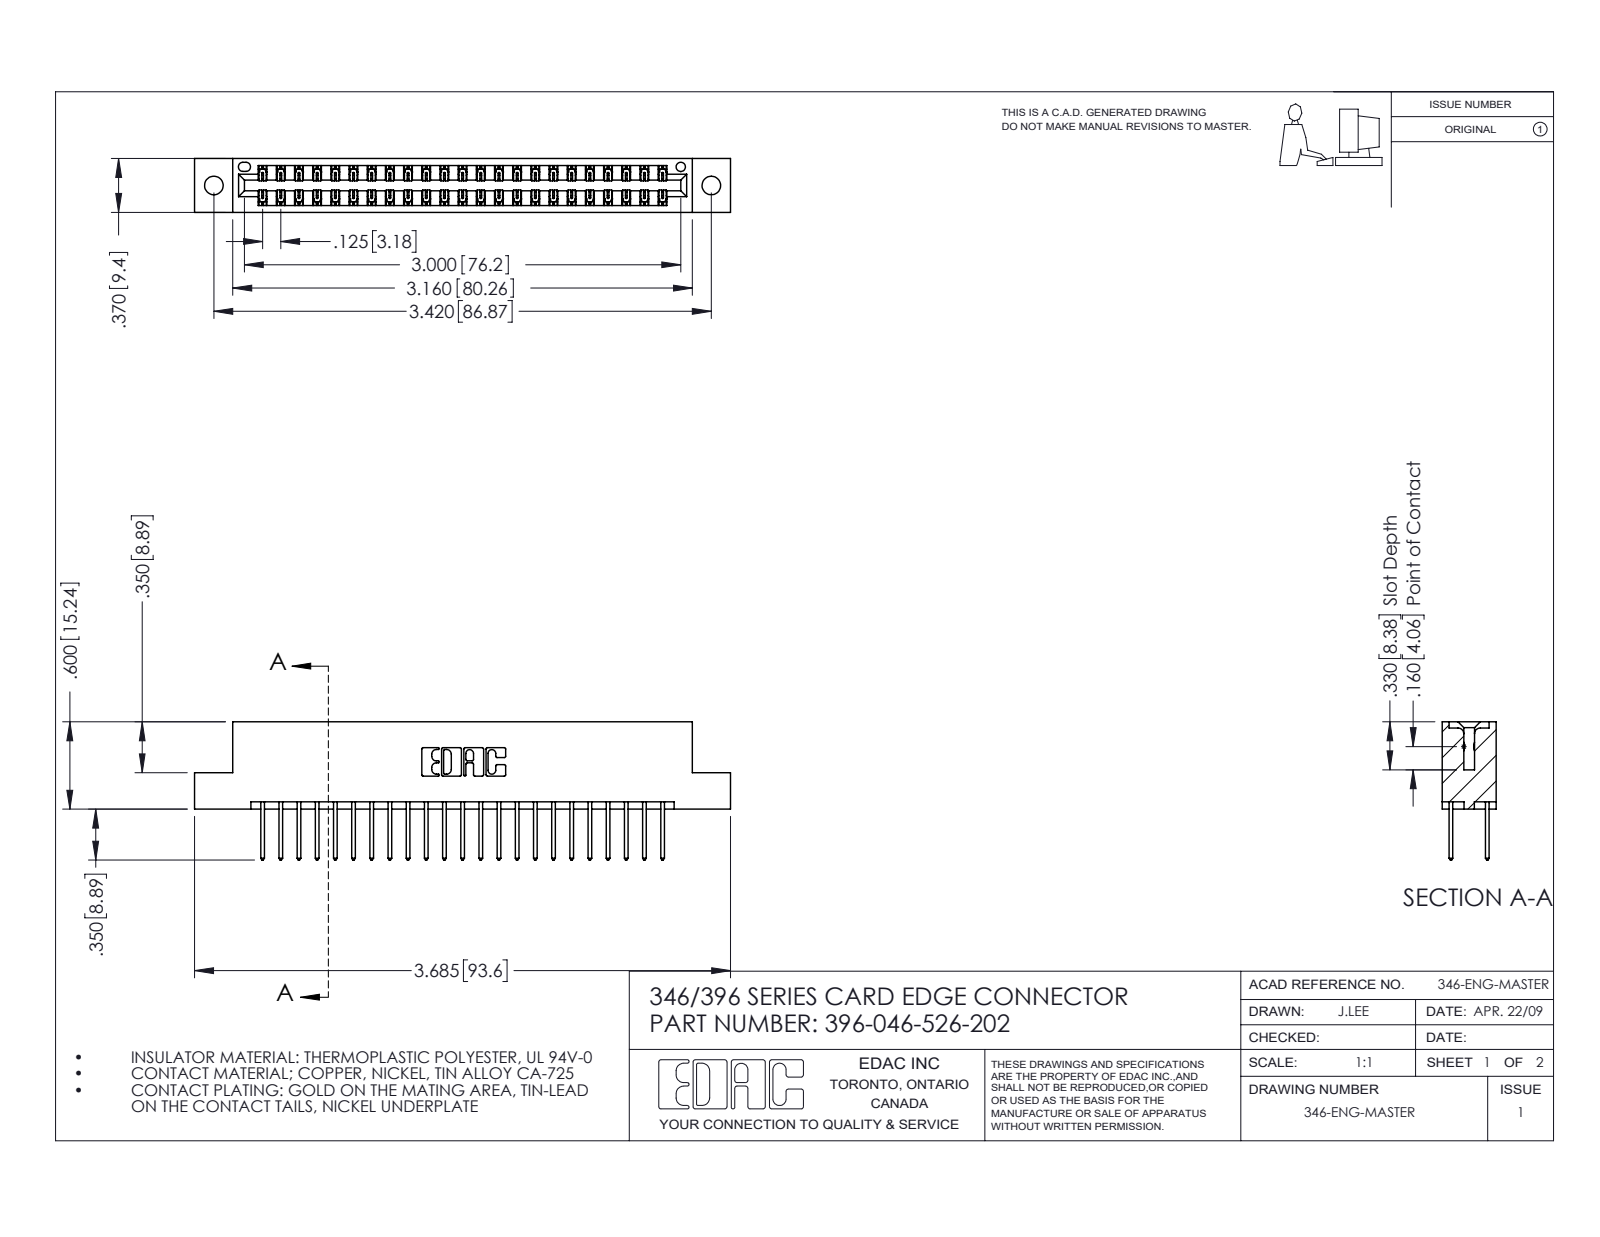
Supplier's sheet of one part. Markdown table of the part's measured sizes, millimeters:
| quantity | value |
| --- | --- |
| part name | 345-292-001_345-293-126; 346 Part_Flush Mounting Lugs - 0.128 Dia; 396-046-526-202 |
| STEP written by | SolidWorks 2016 (CONFIG_CONTROL_DESIGN) |
| units | millimeters |
| bodies | 47 solids, 2514 faces (1686 planar, 828 cylindrical, 0 other) |
| overall size | 93.6 × 24.1 × 9.4 |
| volume | 9 010 mm³ |
| surface area | 12 170 mm² |
| round holes (diameter × count) | 3.3 × 2, 1.6 × 1 |
| partial cylindrical surfaces (radius × count) | 0.2 × 69, 0.3 × 46, 0.3 × 22, 0.2 × 6, 0.8 × 6, 0.7 × 3, 0.4 × 2, 0.6 × 2 |
| main face-to-face distances | 1.2, 8.2, 6.4, 9.4, 1.8, 7.6, 0.6, 7, 3.8, 5.6 |
| hole center spacings | 6.2, 81.6, 86.9 |
